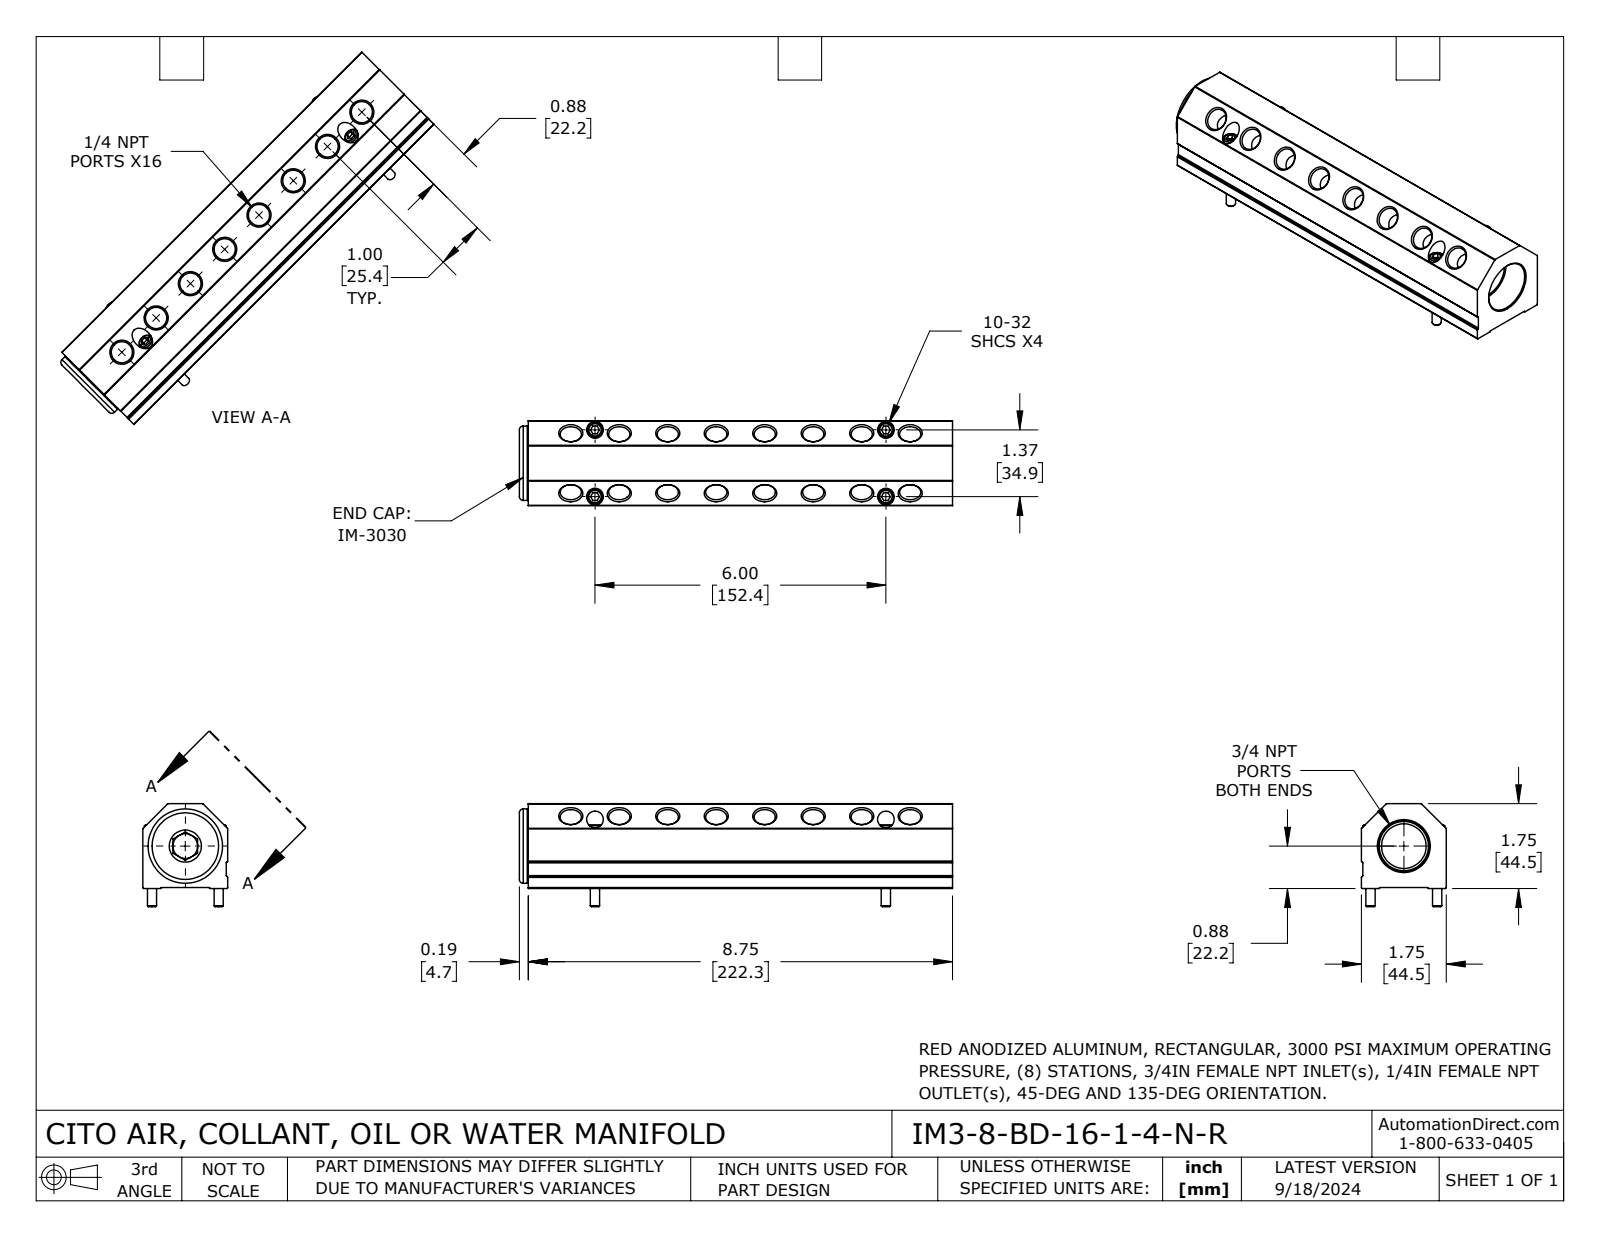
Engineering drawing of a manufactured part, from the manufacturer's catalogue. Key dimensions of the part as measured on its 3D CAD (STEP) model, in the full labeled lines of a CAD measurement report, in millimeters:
Part name (STEP PRODUCT): IM3-8-BD-16-1-4-N-R
STEP written by: SolidWorks 2023 (CONFIG_CONTROL_DESIGN)
Units: millimetres
Bodies: 6 solids, 248 faces (82 planar, 90 cylindrical, 76 other)
Overall size (bounding box): 226.9 × 54 × 44.5
Volume: 288 900 mm³ · Surface area: 68 450 mm²
Round holes (diameter × count): ⌀11.1 ×16, ⌀5.2 ×4, ⌀8.7 ×4, ⌀13 ×1, ⌀23.4 ×1, ⌀35.4 ×1
Round bosses / shafts (diameter × count): ⌀7.9 ×4, ⌀4.8 ×4, ⌀39 ×1, ⌀30 ×1, ⌀23.8 ×1
Partial cylindrical surfaces — rounded edges, fillets, slot ends (radius × count): R0.5 ×14
Main face-to-face distances: 44.5, 43.9, 0.5, 44.5, 0.8, 43.7, 222.3, 4.7, 226.9, 13.5
Hole centre spacings: 25.4, 50.8, 76.2, 101.6, 127, 152.4, 34.9, 156.4
